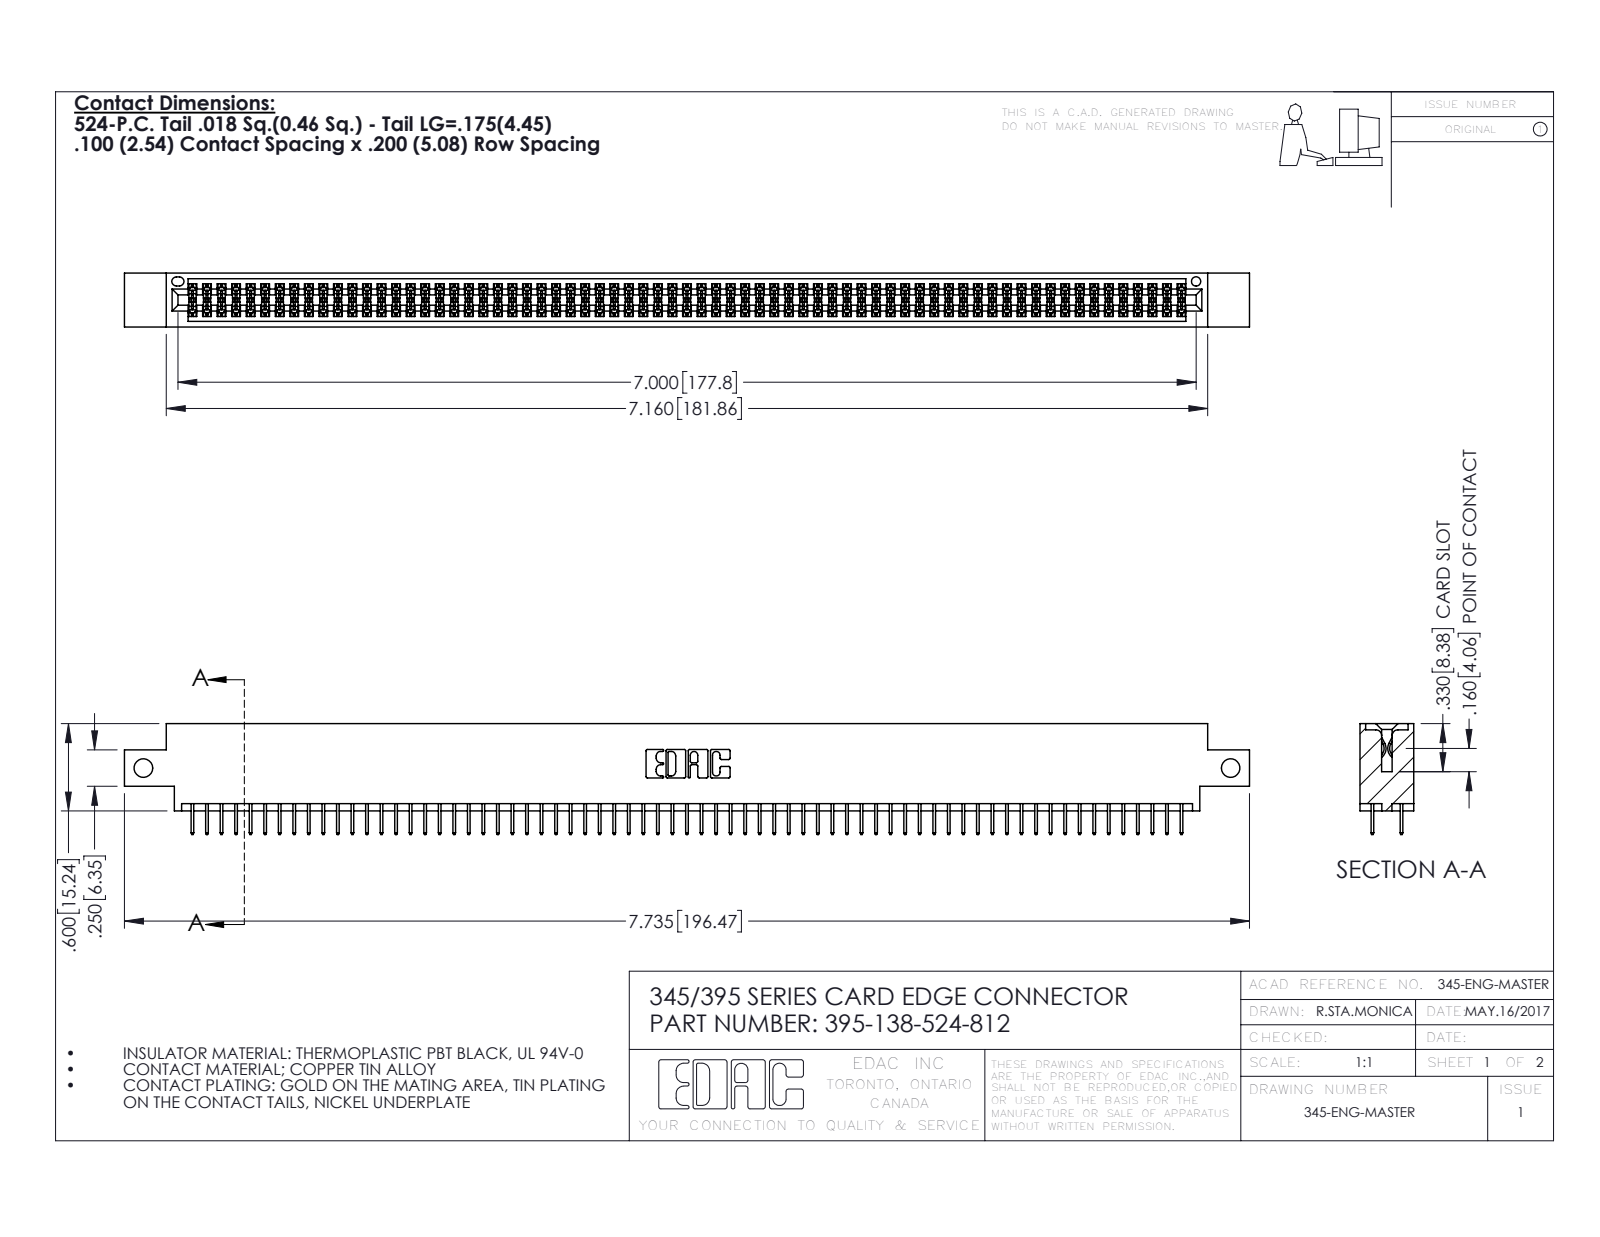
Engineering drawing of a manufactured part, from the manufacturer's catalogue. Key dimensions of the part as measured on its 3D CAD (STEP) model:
Part name (STEP PRODUCT): 345-292-001_345-293-124; 395-138-524-812; 345 Part_0.170 Offset - Side Mount
STEP written by: SolidWorks 2016 (CONFIG_CONTROL_DESIGN)
Units: inches
Bodies: 139 solids, 7582 faces (5466 planar, 2116 cylindrical, 0 other)
Overall size (bounding box): 7.735 × 0.762 × 0.37
Volume: 1.155 in³ · Surface area: 43.33 in²
Round holes (diameter × count): ⌀0.128 ×2, ⌀0.064 ×1
Partial cylindrical surfaces — rounded edges, fillets, slot ends (radius × count): R0.006 ×207, R0.01 ×22, R0.007 ×6, R0.031 ×6, R0.026 ×3, R0.014 ×2, R0.019 ×2, R0.022 ×2
Main face-to-face distances: 0.072, 0.298, 0.2, 0.37, 0.098, 0.272, 0.025, 0.225, 0.072, 0.175
Hole centre spacings: 7.475
